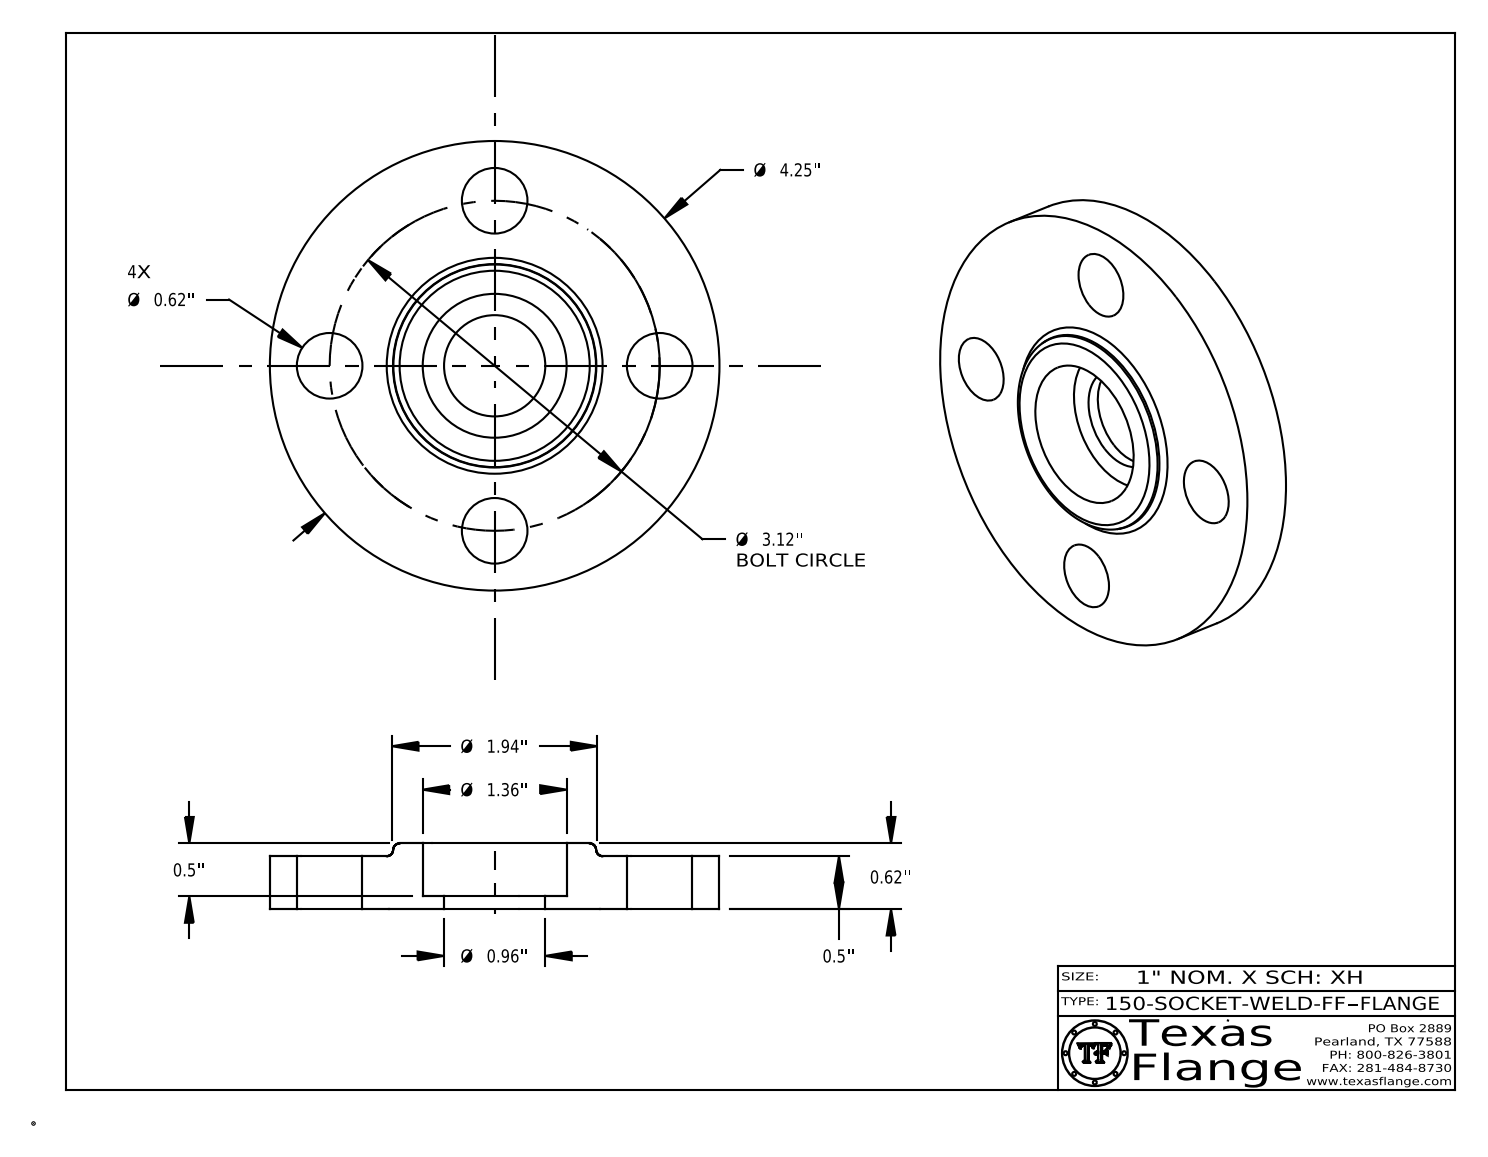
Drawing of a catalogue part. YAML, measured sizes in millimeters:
part_name: "150-SOCKET-WELD-FF"
step_written_by: "CATIA V5 STEP AP214 (AUTOMOTIVE_DESIGN)"
units: millimeters
bodies: {solids: 1, faces: 410, planar: 370, cylindrical: 34, other: 6}
overall_size: [108, 108, 15.7]
volume: 98700
surface_area: 24570
round_holes:
  - {diameter: 15.7, count: 4}
  - {diameter: 12.6, count: 1}
  - {diameter: 24.3, count: 1}
  - {diameter: 34.5, count: 1}
round_bosses_or_shafts:
  - {diameter: 0.8, count: 8}
  - {diameter: 108, count: 1}
  - {diameter: 9.9, count: 1}
face_to_face_distances: [12.7, 3, 15.7, 9.7, 12.3, 9.3, 0.4, 3.4, 3.8, 3.7]
hole_center_spacings: [39.6, 56, 30.3, 73.2, 79.2, 39.6]
